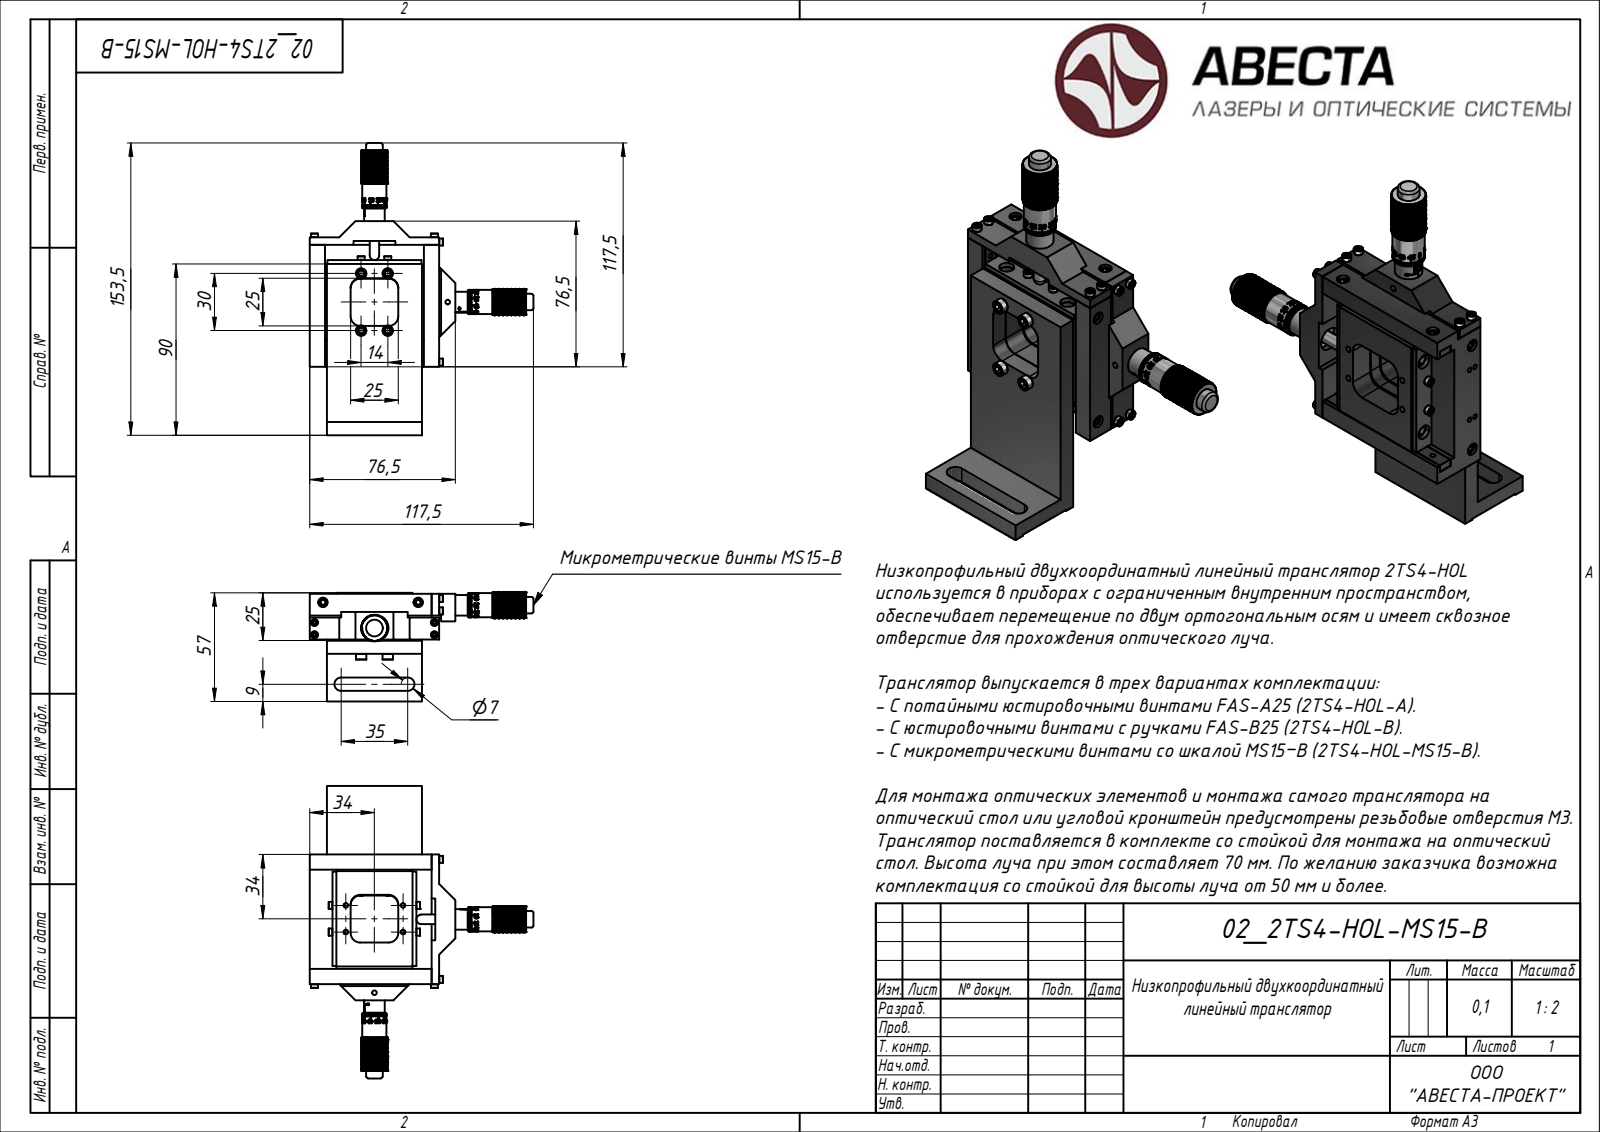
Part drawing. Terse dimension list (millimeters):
written by: Rhino 7.34 (AUTOMOTIVE_DESIGN)
unit: mm
bodies: 18 solids, 7624 faces (6332 planar, 650 cylindrical, 642 other)
size: 153.5 × 117.5 × 57.45
volume: 116 377 mm³; area: 68 907 mm²
holes: 7× ⌀2.01, 7× ⌀2.46, 4× ⌀5, 4× ⌀6, 3× ⌀2.01, 2× ⌀1.57, 2× ⌀2.46, 2× ⌀3, 2× ⌀5.5, 2× ⌀9.55, 2× ⌀11, 1× ⌀1.57
bosses: 14× ⌀3, 12× ⌀3.7, 5× ⌀2, 4× ⌀5.4, 4× ⌀4.5, 2× ⌀13.5, 2× ⌀12.7, 2× ⌀10.8
rounds: 8× R3, 8× R5, 5× R1.01, 5× R1.23, 5× R1.23, 4× R1.1, 3× R0.78, 3× R0.78
face distances: 15, 9.5, 9, 7.5, 10, 5, 0.5, 7, 2, 8
hole spacings: 33.11, 3, 15.07, 19.21, 31.69, 35.03, 6.67, 11.1
